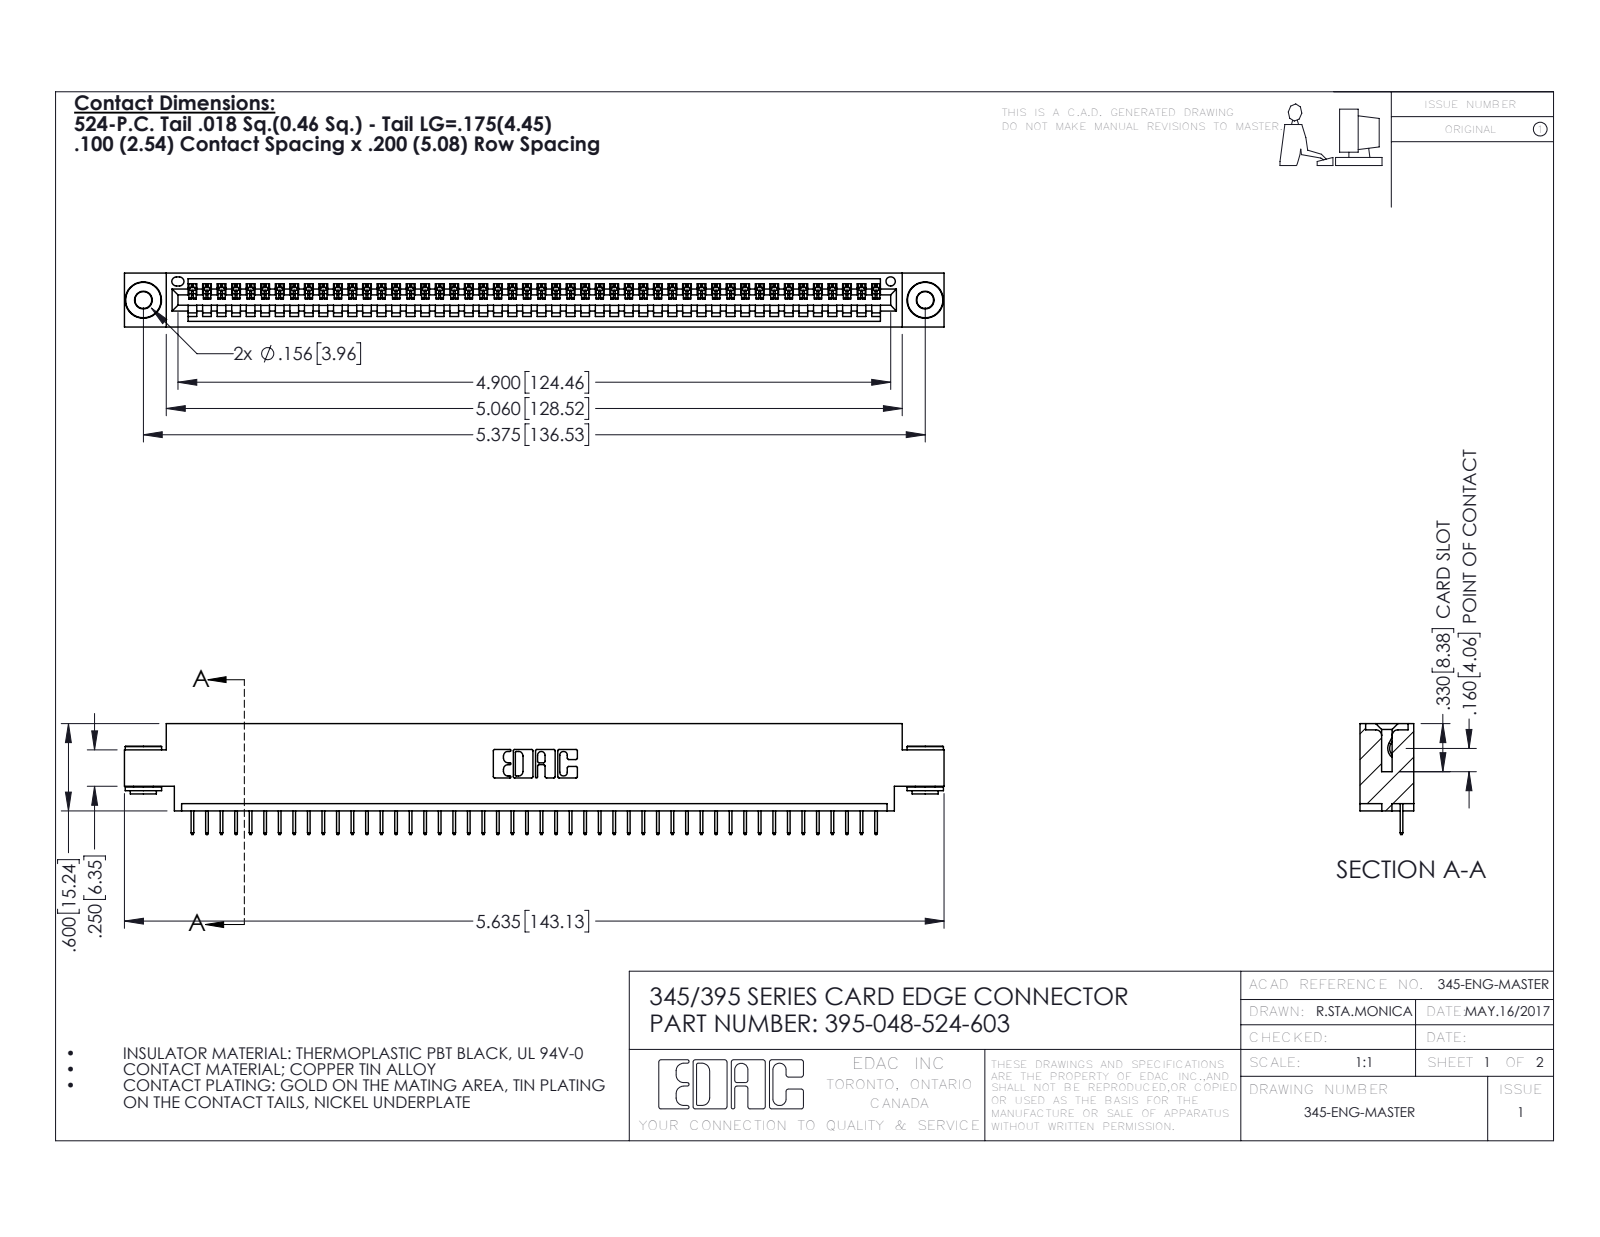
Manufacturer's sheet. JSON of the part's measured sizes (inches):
{"part_name": "345 Part_0.170 Offset - 0.156 Dia-TH; 345-292-001_345-293-124; 395-048-524-603; 345-250-002_345-250-002-102", "step_written_by": "SolidWorks 2016 (CONFIG_CONTROL_DESIGN)", "units": "inches", "bodies": {"solids": 51, "faces": 3144, "planar": 2302, "cylindrical": 834, "other": 8}, "overall_size": [5.635, 0.762, 0.37], "volume_in3": 0.815, "surface_area_in2": 27.23, "round_holes": [[0.116, 2], [0.156, 2], [0.064, 1]], "round_bosses_or_shafts": [[0.25, 2], [0.18, 2], [0.136, 2]], "partial_cylinders_radius": [[0.006, 96], [0.01, 22], [0.007, 6], [0.031, 6], [0.026, 3], [0.031, 2], [0.04, 2], [0.014, 1]], "face_to_face_distances": [0.072, 0.298, 0.37, 0.2, 0.098, 0.272, 0.025, 0.225, 0.072, 0.175], "hole_center_spacings": [0.27, 5.139, 5.375]}
